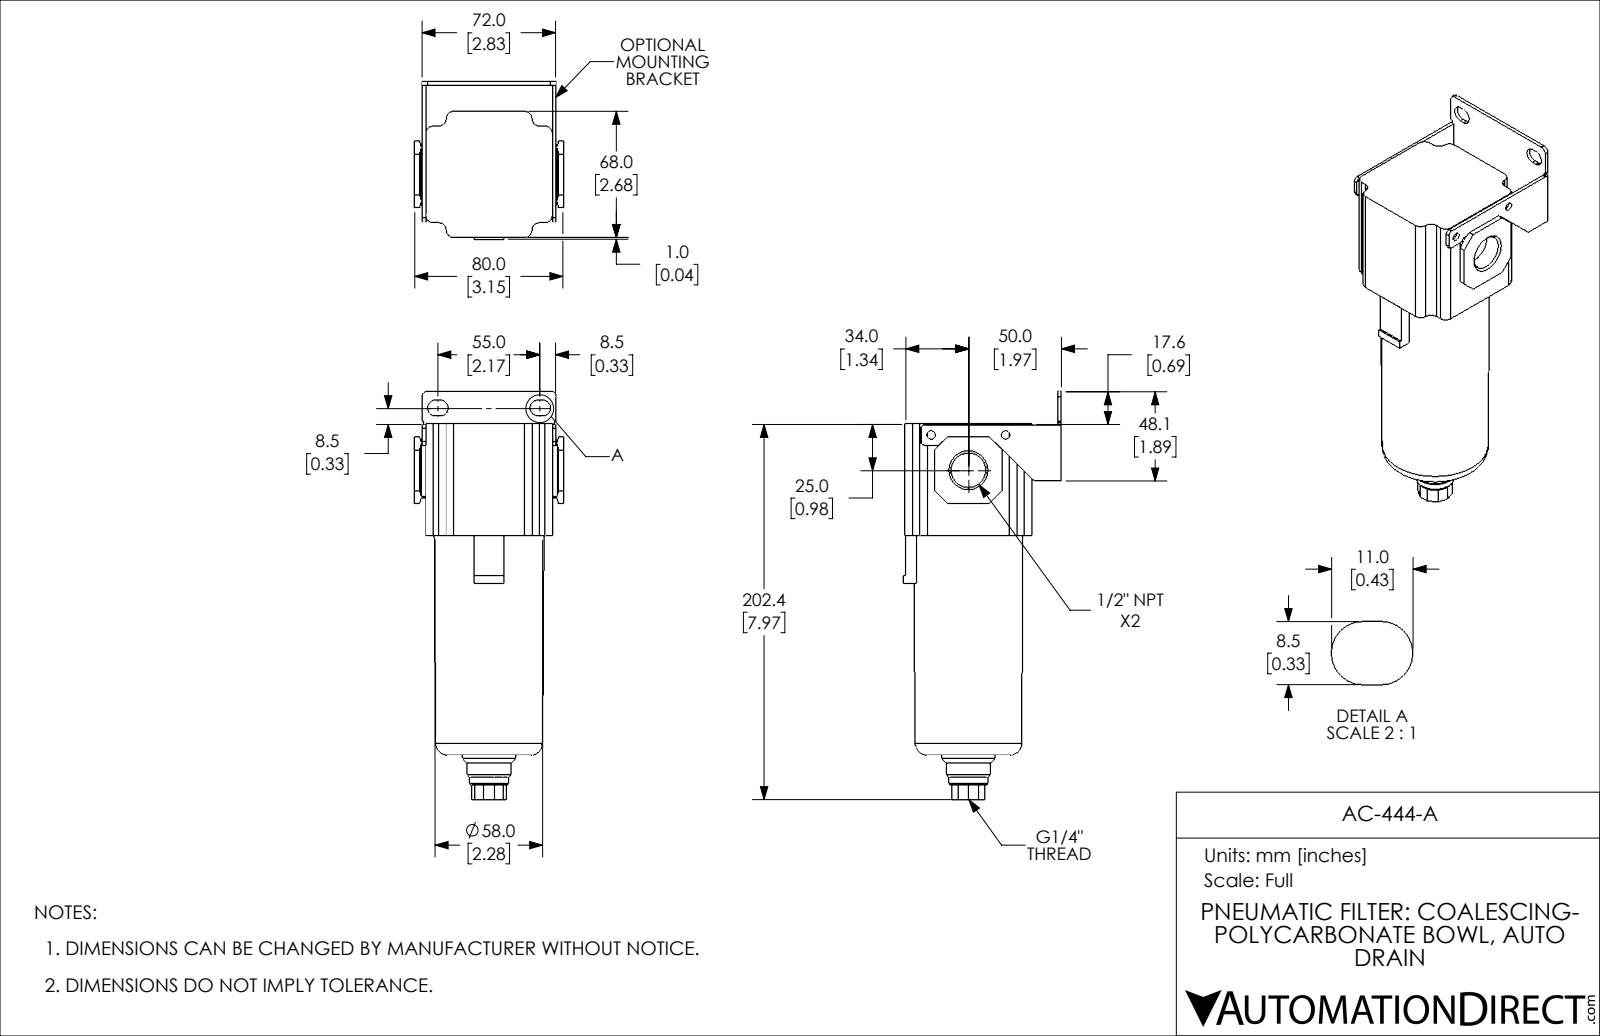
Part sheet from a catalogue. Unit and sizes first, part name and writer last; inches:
Units: inches
Overall size (bounding box): 8.661 × 3.346 × 3.15
Round holes (diameter × count): ⌀0.177 ×2, ⌀0.451 ×1, ⌀0.734 ×1
Round bosses / shafts (diameter × count): ⌀1.102 ×1, ⌀0.906 ×1, ⌀0.787 ×1
Partial cylindrical surfaces — rounded edges, fillets, slot ends (radius × count): R0.157 ×12, R0.167 ×4, R0.079 ×3, R0.039 ×2, R0.118 ×2
Main face-to-face distances: 0.079, 2.677, 2.756, 0.63, 2.362, 3.307, 0.551, 3.228, 0.157, 0.236
Hole centre spacings: 1.086, 1.575
Volume: 35.81 in³ · Surface area: 94.13 in²
Bodies: 1 solid, 166 faces (102 planar, 48 cylindrical, 16 other)
Part name (STEP PRODUCT): AC-444-A
STEP written by: SolidWorks 2018 (AUTOMOTIVE_DESIGN)
